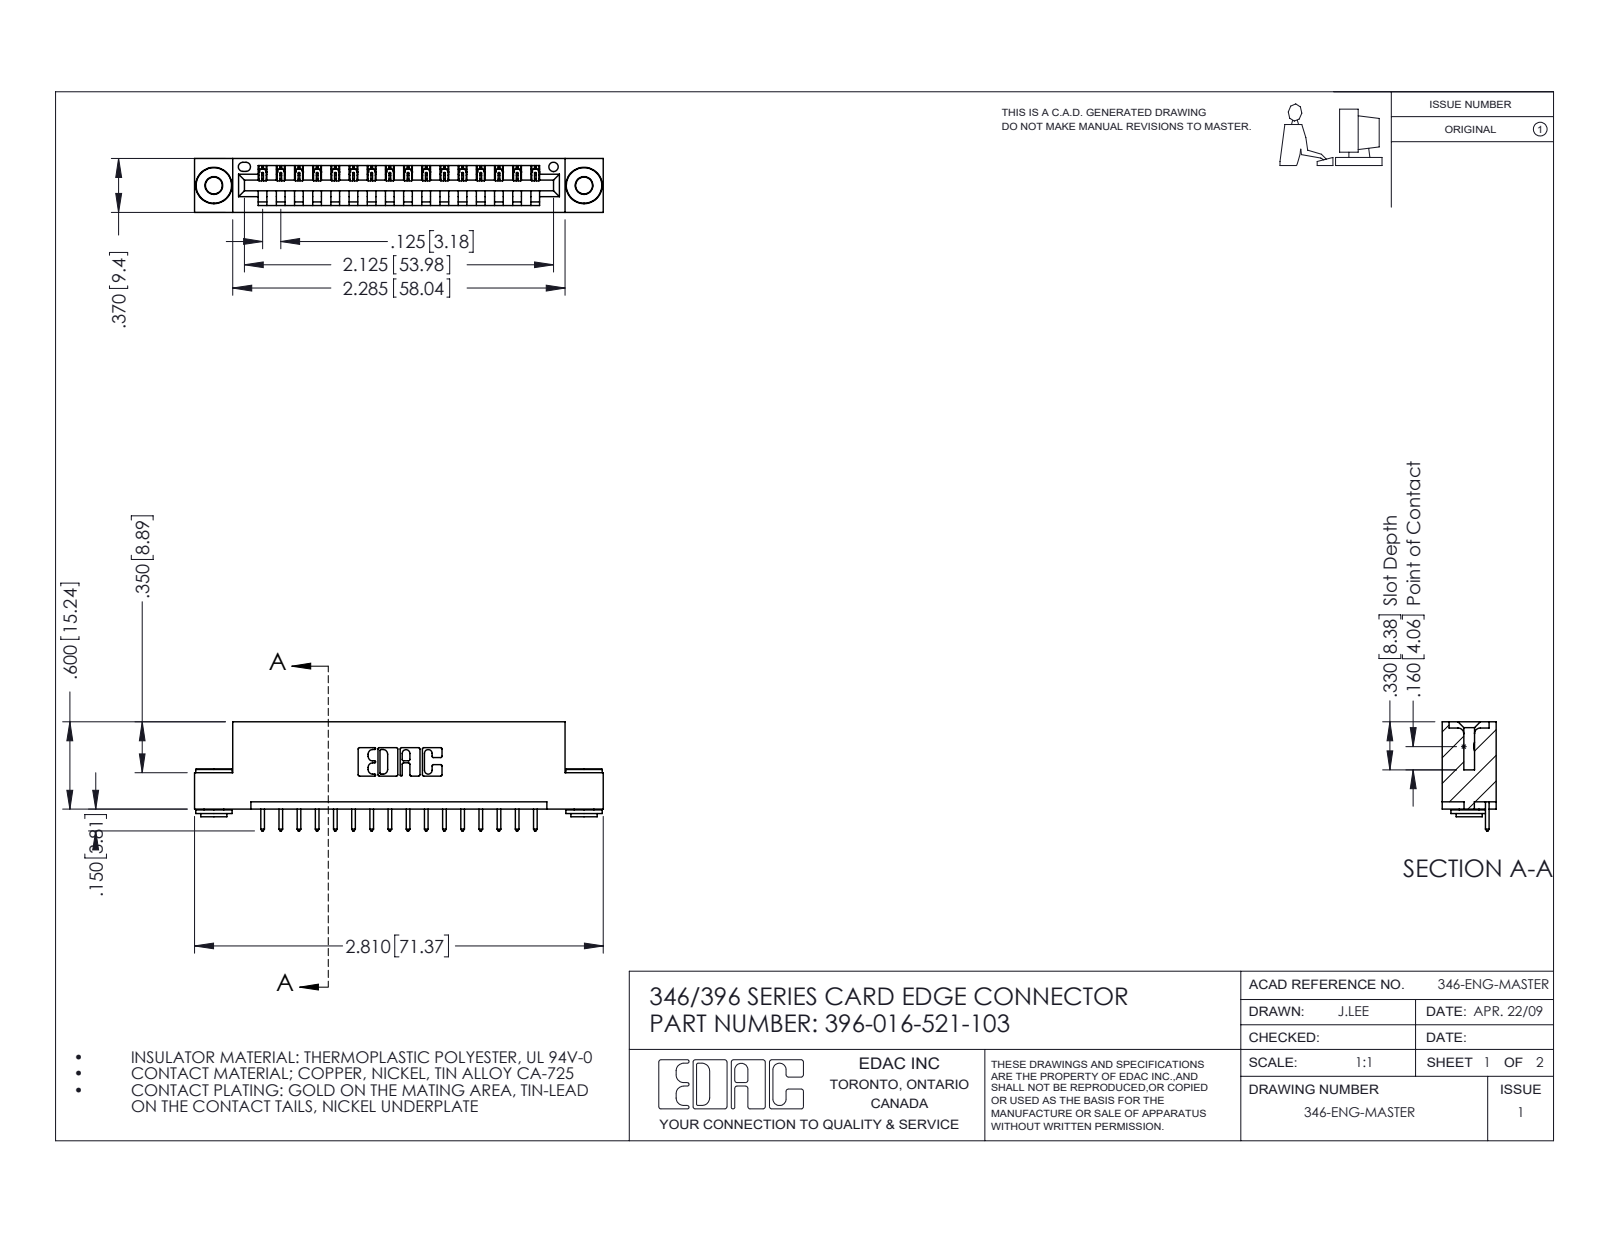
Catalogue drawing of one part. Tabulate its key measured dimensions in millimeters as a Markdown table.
| quantity | value |
| --- | --- |
| part name | 346 Part_Flush Mounting Lugs - 0.156 Dia-TH; 345-250-002_345-250-002-102; 396-016-521-103; 345-292-001_345-293-121 |
| STEP written by | SolidWorks 2016 (CONFIG_CONTROL_DESIGN) |
| units | millimeters |
| bodies | 19 solids, 1088 faces (726 planar, 354 cylindrical, 8 other) |
| overall size | 71.4 × 19.1 × 9.4 |
| volume | 6 620 mm³ |
| surface area | 8 039 mm² |
| round holes (diameter × count) | 2.9 × 2, 4 × 2, 1.6 × 1 |
| round bosses / shafts (diameter × count) | 6.4 × 2, 4.6 × 2, 3.5 × 2 |
| partial cylindrical surfaces (radius × count) | 0.2 × 32, 0.3 × 32, 0.3 × 22, 0.2 × 6, 0.8 × 6, 0.7 × 3, 0.8 × 2, 1 × 2 |
| main face-to-face distances | 6.4, 1.2, 8.2, 9.4, 0.6, 1.8, 7.6, 3.8, 5.6, 2.5 |
| hole center spacings | 6.2, 59.4, 64.6 |
